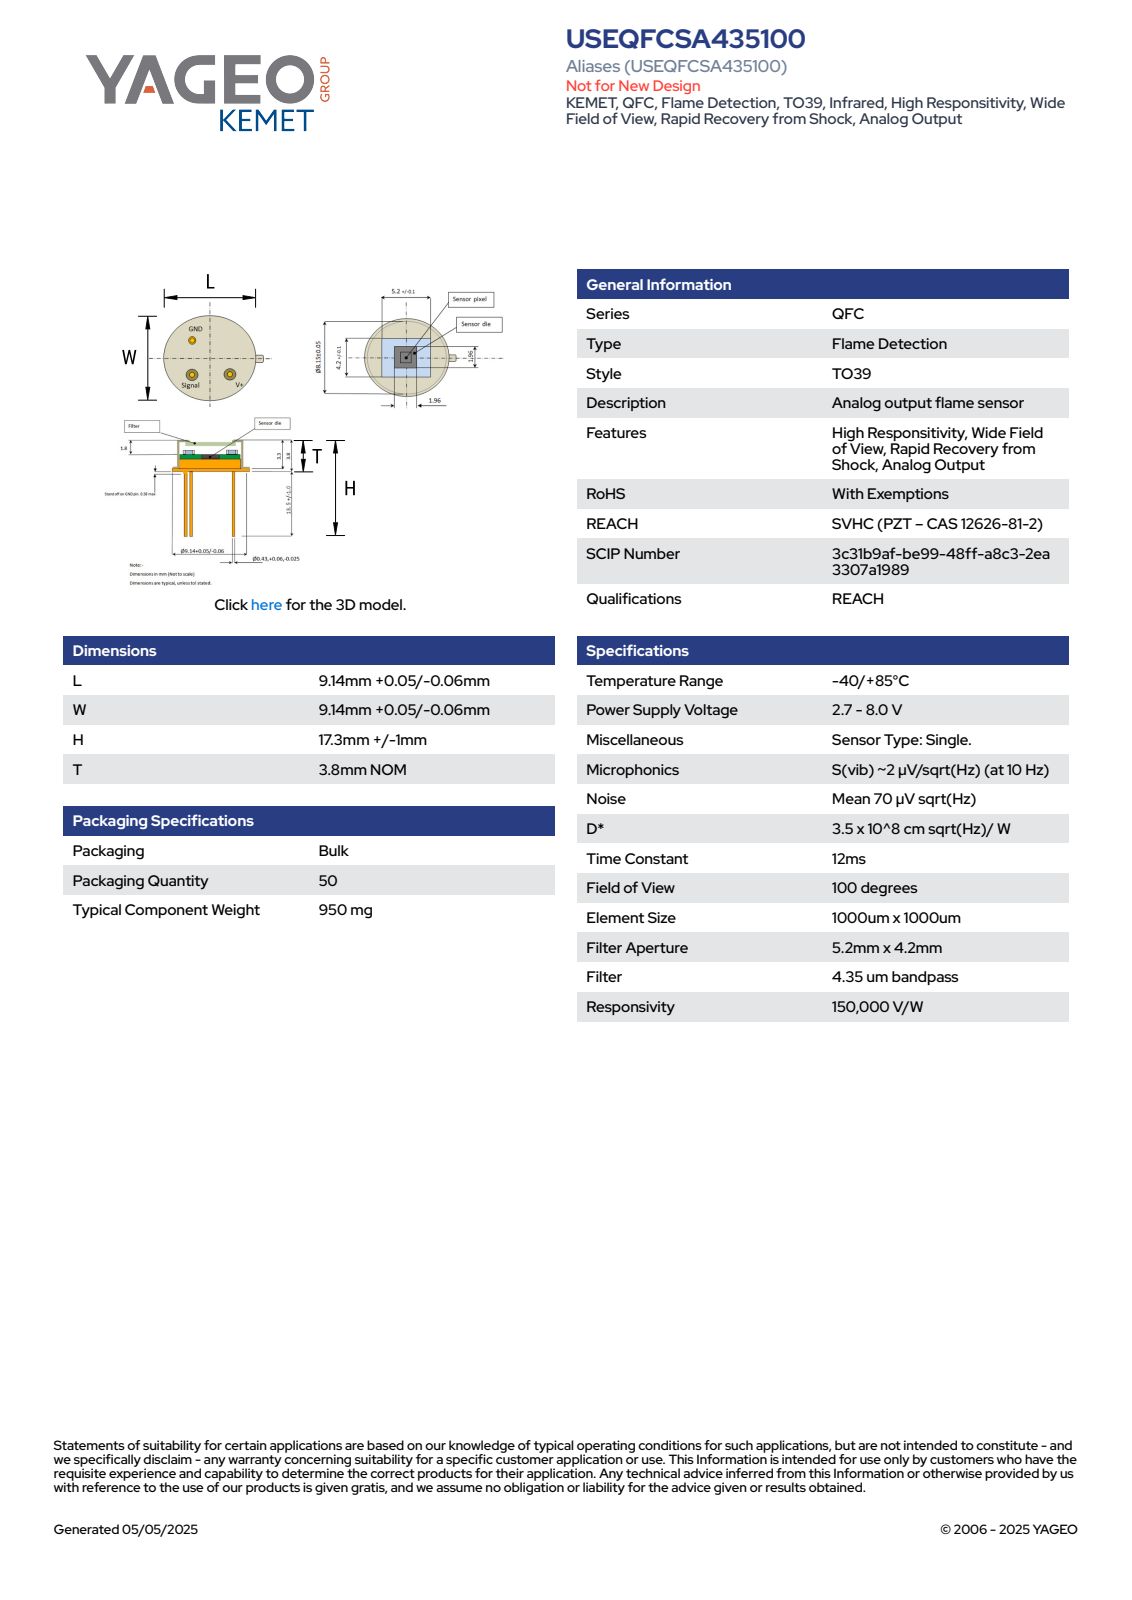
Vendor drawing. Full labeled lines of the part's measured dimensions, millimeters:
Part name (STEP PRODUCT): Default
STEP written by: SolidWorks 2014 (AUTOMOTIVE_DESIGN)
Units: millimetres
Bodies: 1 solid, 79 faces (68 planar, 11 cylindrical, 0 other)
Overall size (bounding box): 18.3 × 9.68 × 9.19
Volume: 216 mm³ · Surface area: 300 mm²
Round bosses / shafts (diameter × count): ⌀0.49 ×3, ⌀9.19 ×1, ⌀8.2 ×1
Main face-to-face distances: 3.8, 0.5, 3.3, 14.5, 15, 18.3, 0.44, 1.88, 2.32, 4.2
